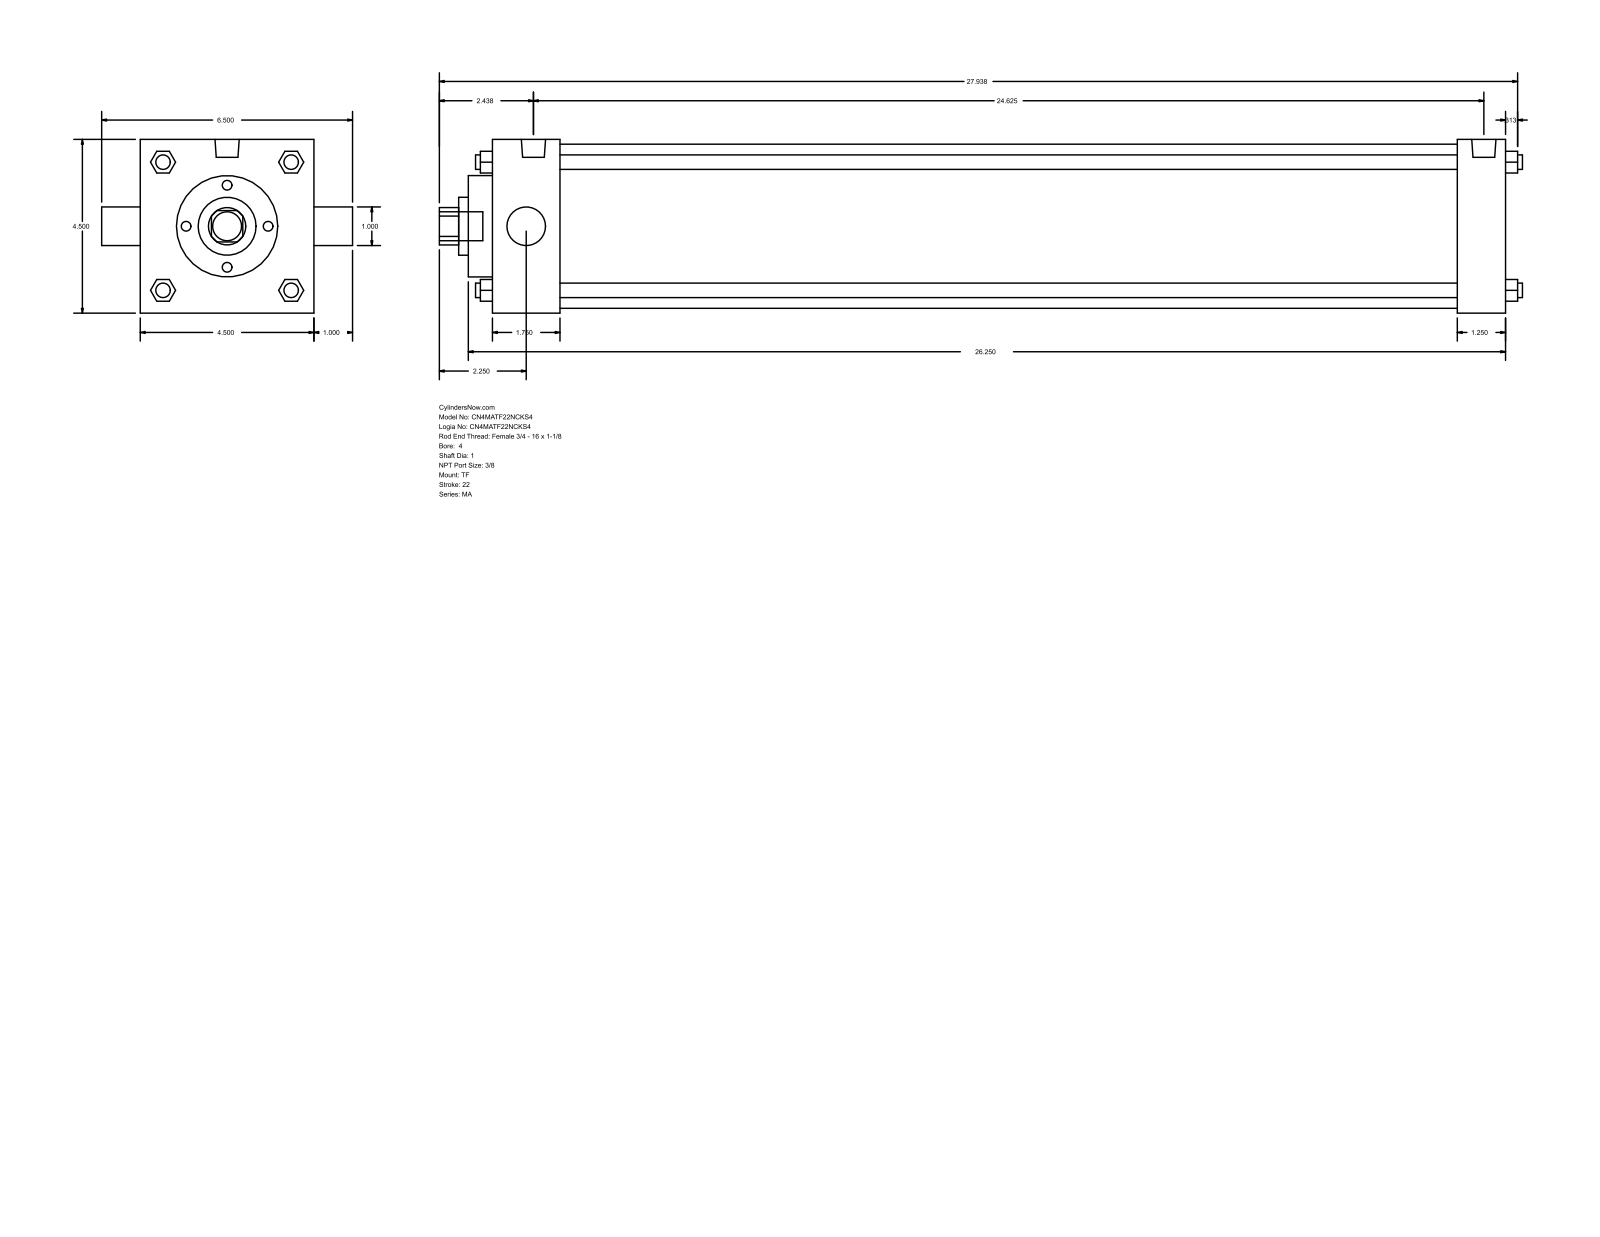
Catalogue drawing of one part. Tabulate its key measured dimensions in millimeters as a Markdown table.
| quantity | value |
| --- | --- |
| part name | MA_TF__0400_1 |
| STEP written by | GSSL Pune (CONFIG_CONTROL_DESIGN) |
| units | millimeters |
| bodies | 0 solids, 122 faces (93 planar, 29 cylindrical, 0 other) |
| overall size | 712.79 × 165.1 × 114.3 |
| round holes (diameter × count) | 25.4 × 2, 38.1 × 1, 66.67 × 1, 107.95 × 1 |
| round bosses / shafts (diameter × count) | 9.53 × 4, 11.11 × 3, 15.93 × 2, 19.05 × 1 |
| partial cylindrical surfaces (radius × count) | 12.29 × 1 |
| main face-to-face distances | 114.3, 666.75, 635, 31.75, 44.46, 590.54, 622.29, 682.62, 15.87, 60.33 |
